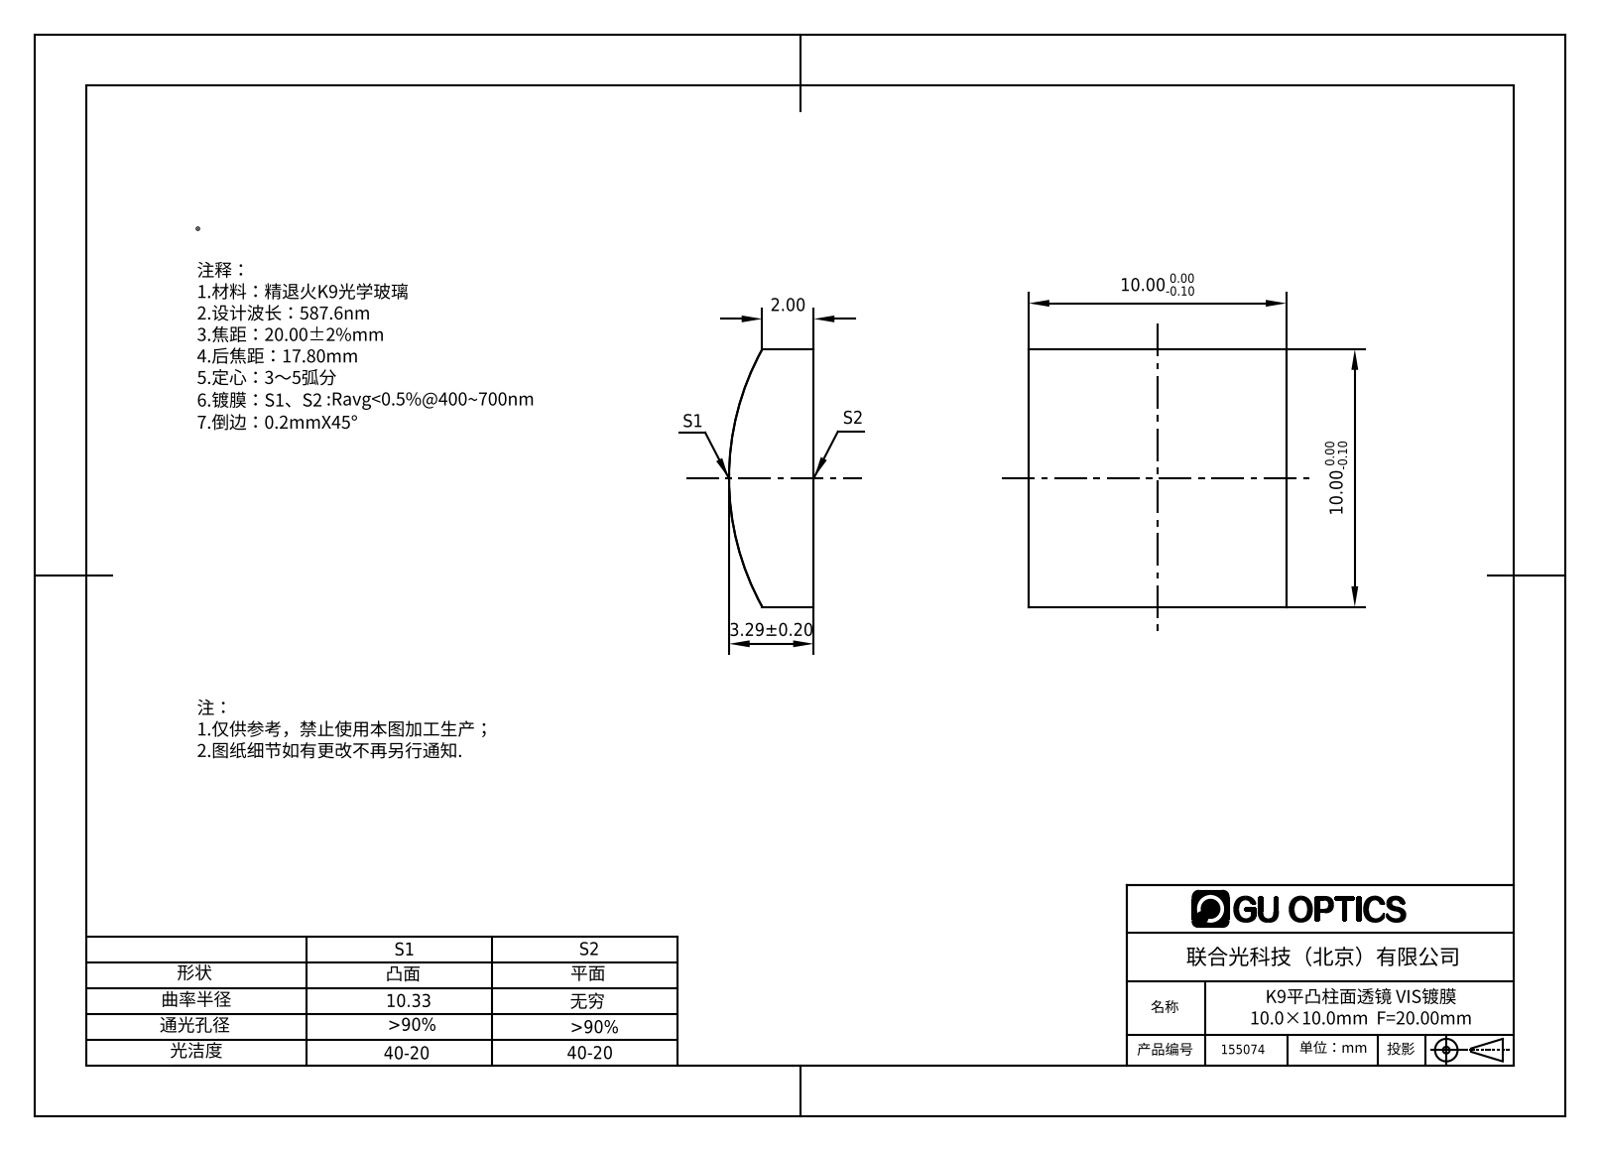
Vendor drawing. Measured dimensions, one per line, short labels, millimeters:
name: 155008
written by: SolidWorks 2016 (AUTOMOTIVE_DESIGN)
unit: mm
bodies: 1 solid, 6 faces (5 planar, 1 cylindrical, 0 other)
size: 10 × 10 × 3.29
volume: 287 mm³; area: 302 mm²
rounds: 1× R10.33
face distances: 10
